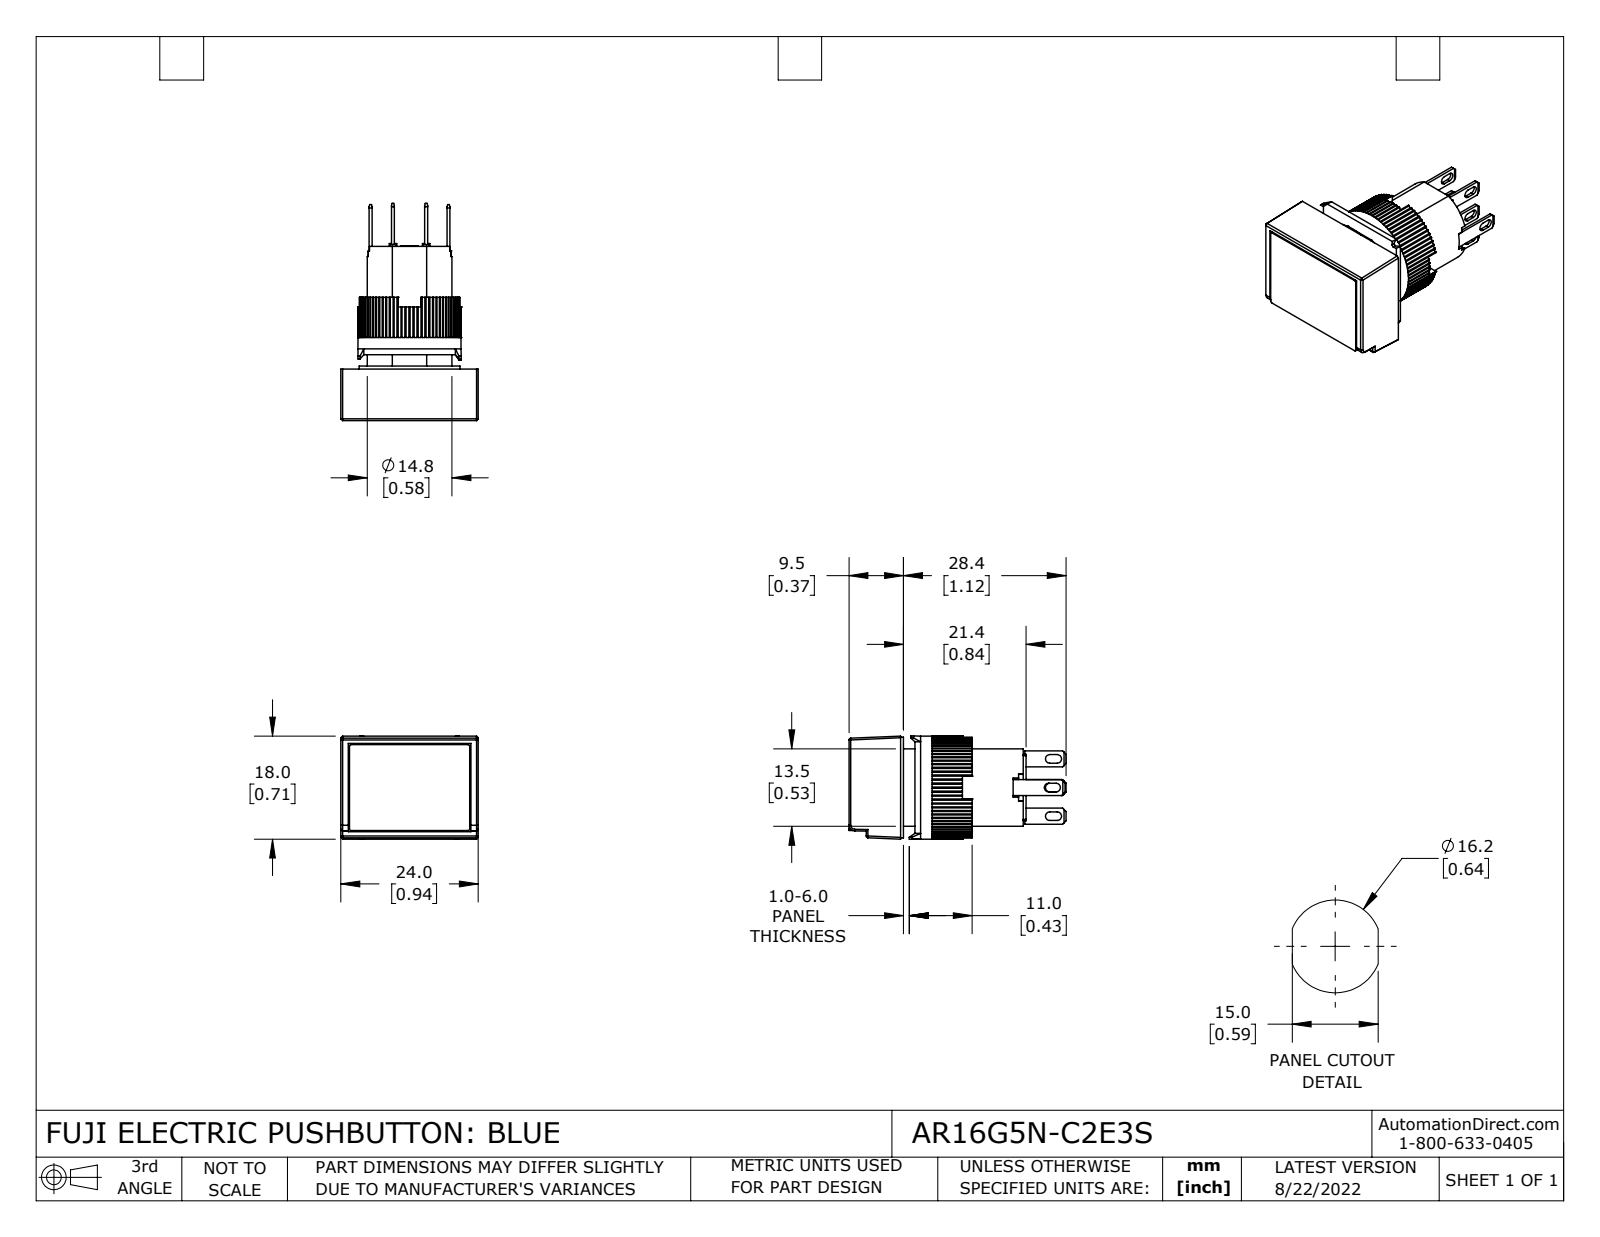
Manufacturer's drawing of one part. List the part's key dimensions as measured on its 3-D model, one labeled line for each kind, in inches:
Part name (STEP PRODUCT): AR16G5N-C2E3S
STEP written by: SolidWorks 2021 (CONFIG_CONTROL_DESIGN)
Units: inches
Bodies: 14 solids, 841 faces (654 planar, 181 cylindrical, 6 other)
Overall size (bounding box): 1.492 × 0.945 × 0.709
Volume: 0.448 in³ · Surface area: 9.503 in²
Round holes (diameter × count): ⌀0.543 ×1, ⌀0.583 ×1
Round bosses / shafts (diameter × count): ⌀0.709 ×1, ⌀0.693 ×1
Partial cylindrical surfaces — rounded edges, fillets, slot ends (radius × count): R0.01 ×80, R0.008 ×12, R0.03 ×8, R0.012 ×6, R0.039 ×1
Main face-to-face distances: 0.213, 0.354, 0.142, 0.35, 0.492, 0.138, 0.02, 0.843, 0.059, 0.453
